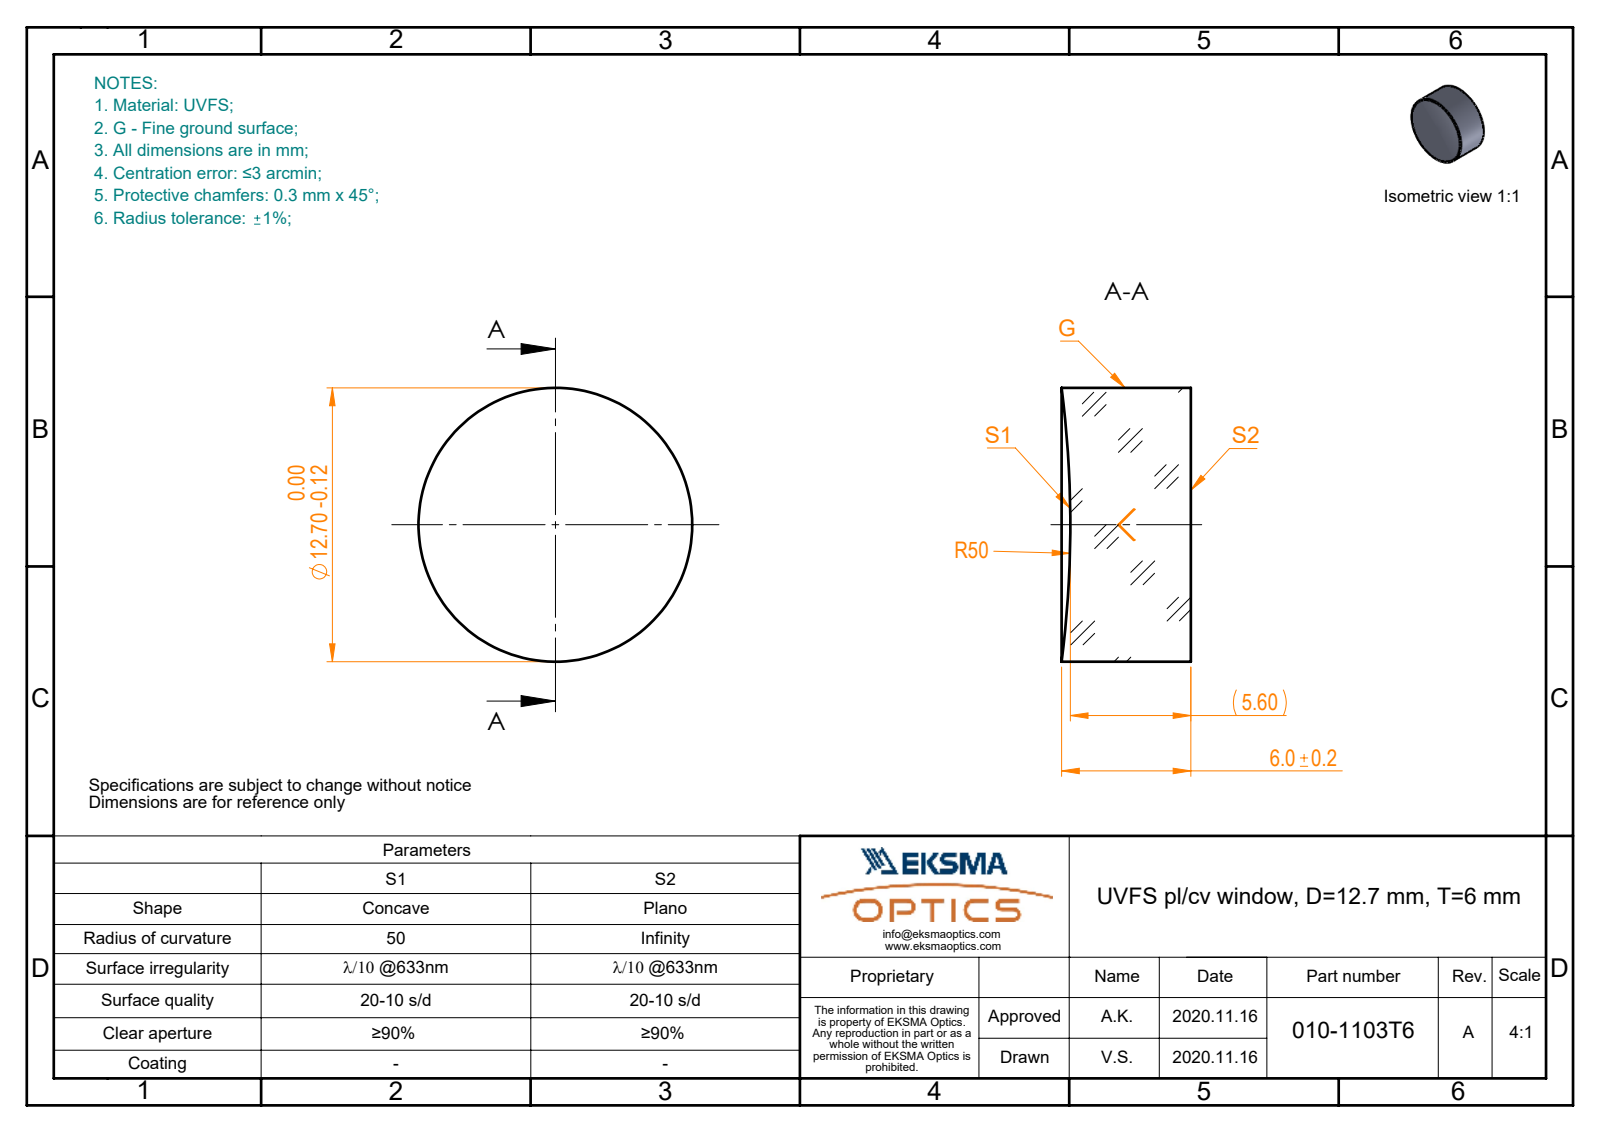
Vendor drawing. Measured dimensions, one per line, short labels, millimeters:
name: 010-1103T6_UVFS_PCV_window
written by: SolidWorks 2019 (CONFIG_CONTROL_DESIGN)
unit: mm
bodies: 1 solid, 5 faces (1 planar, 2 cylindrical, 2 other)
size: 12.7 × 12.7 × 6
volume: 734 mm³; area: 493 mm²
bosses: 1× ⌀12.7
